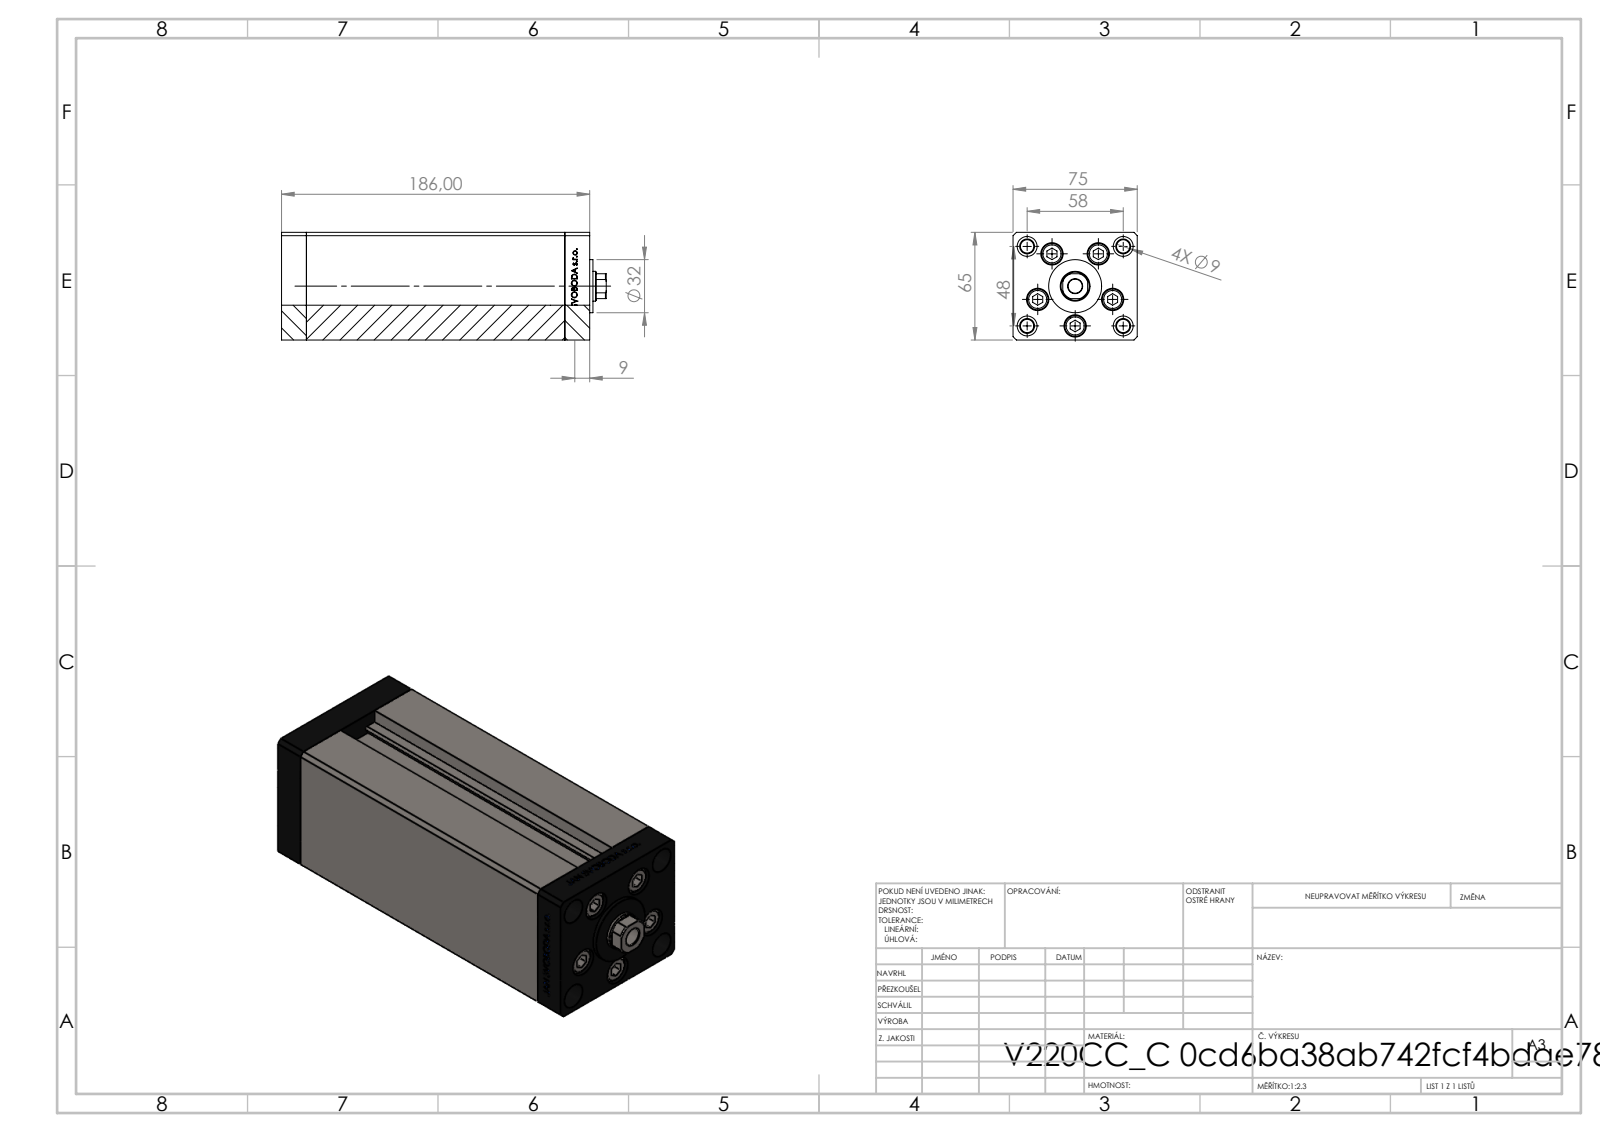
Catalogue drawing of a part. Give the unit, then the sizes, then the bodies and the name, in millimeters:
Units: millimetres
Overall size (bounding box): 196 × 75 × 65
Round holes (diameter × count): ⌀9 ×9, ⌀13.5 ×5, ⌀8 ×4, ⌀12 ×4, ⌀8.5 ×1, ⌀12.5 ×1, ⌀18 ×1
Round bosses / shafts (diameter × count): ⌀8 ×5, ⌀12.5 ×4, ⌀32 ×1
Partial cylindrical surfaces — rounded edges, fillets, slot ends (radius × count): R0.93 ×2, R8.5 ×1
Main face-to-face distances: 75, 65, 15, 156, 171, 186, 28, 54.5, 10.5, 26.25
Hole centre spacings: 24, 37.64, 15.67, 17.22, 27.71, 28.83, 29, 32.63
Volume: 761 493 mm³ · Surface area: 152 717 mm²
Bodies: 13 solids, 1159 faces (538 planar, 159 cylindrical, 462 other)
Part name (STEP PRODUCT): V220C_VC_C; ALLEN BOLT; V220C FRONT; V220C BACK_C (+1 more)
STEP written by: SolidWorks 2019 (CONFIG_CONTROL_DESIGN)
